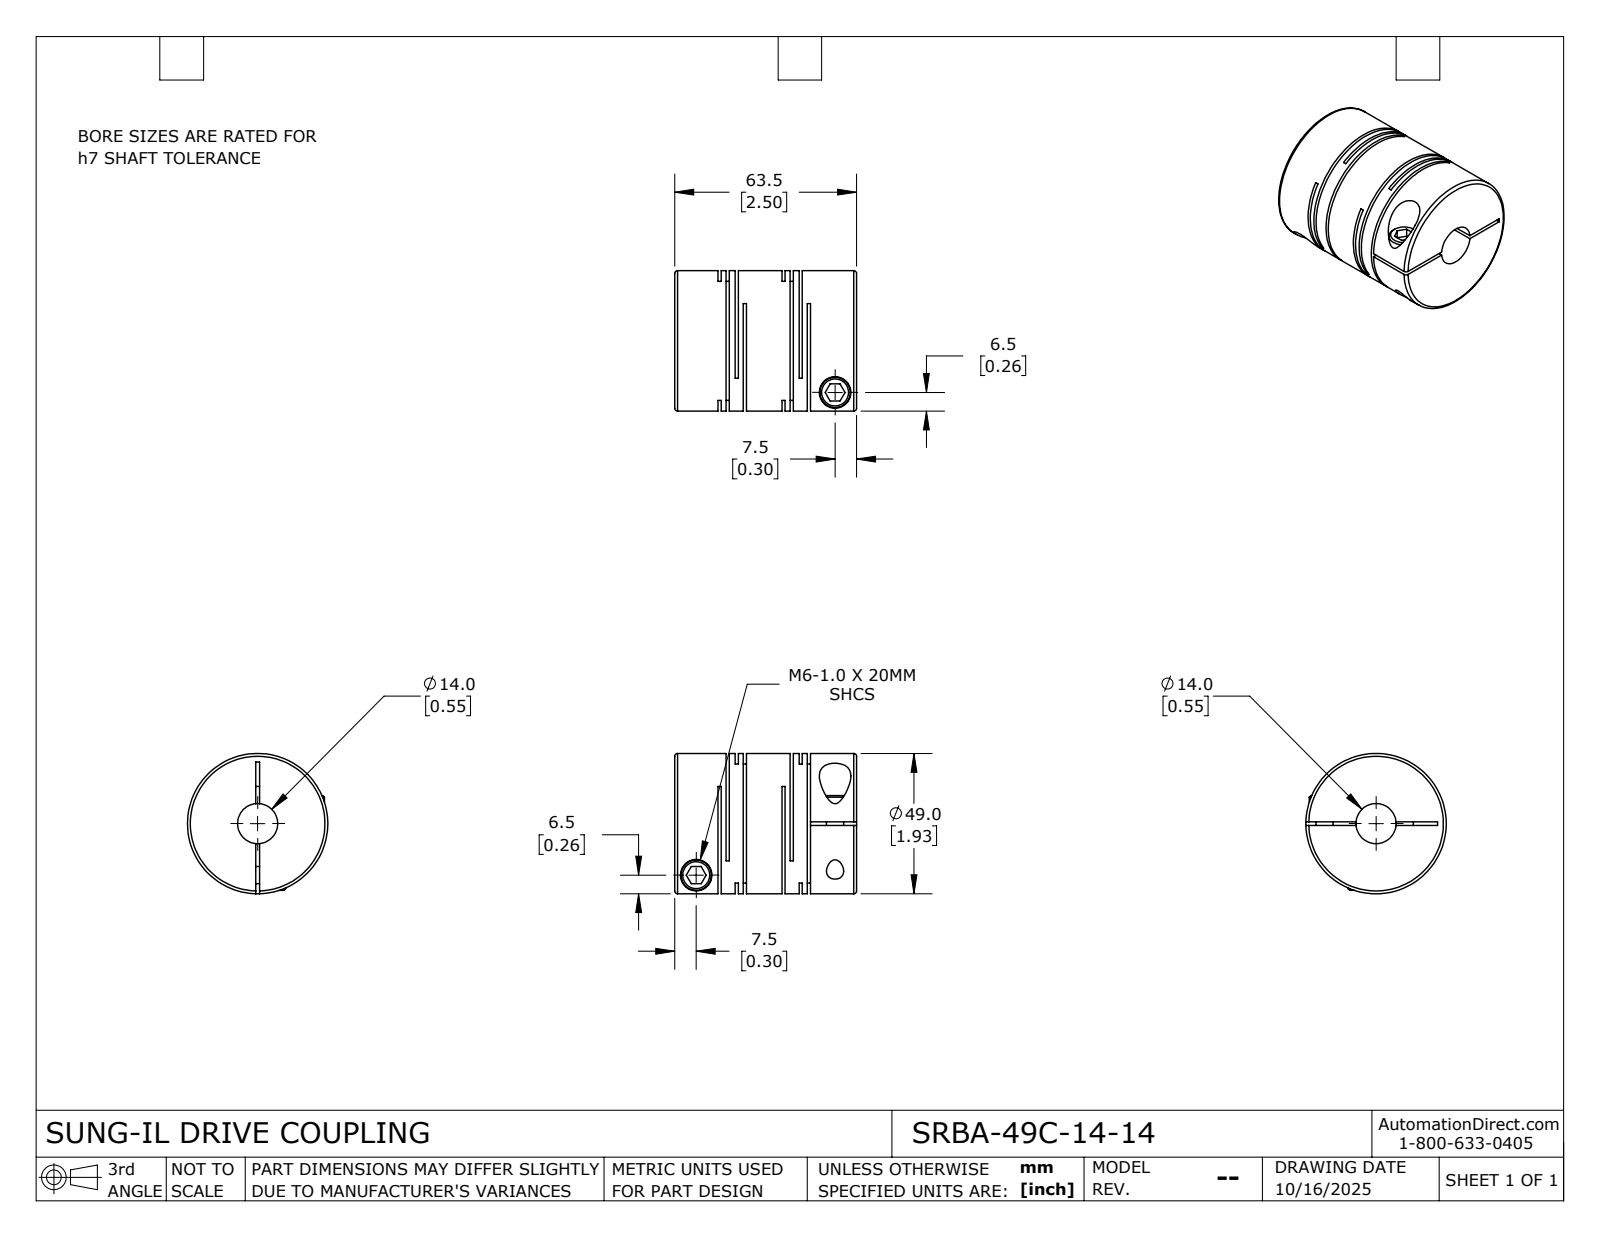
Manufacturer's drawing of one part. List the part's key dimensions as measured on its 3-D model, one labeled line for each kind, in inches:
Part name (STEP PRODUCT): SRBA-49C-14-14
STEP written by: SolidWorks 2024 (CONFIG_CONTROL_DESIGN)
Units: inches
Bodies: 1 solid, 115 faces (60 planar, 42 cylindrical, 13 other)
Overall size (bounding box): 2.5 × 1.929 × 1.929
Volume: 5.781 in³ · Surface area: 62.27 in²
Round holes (diameter × count): ⌀0.236 ×2, ⌀0.433 ×2, ⌀0.551 ×1
Round bosses / shafts (diameter × count): ⌀0.417 ×2, ⌀1.929 ×1
Main face-to-face distances: 0.236, 0.043, 0.88, 0.112, 0.837, 0.124, 0.069, 0.193, 0.768, 0.644
